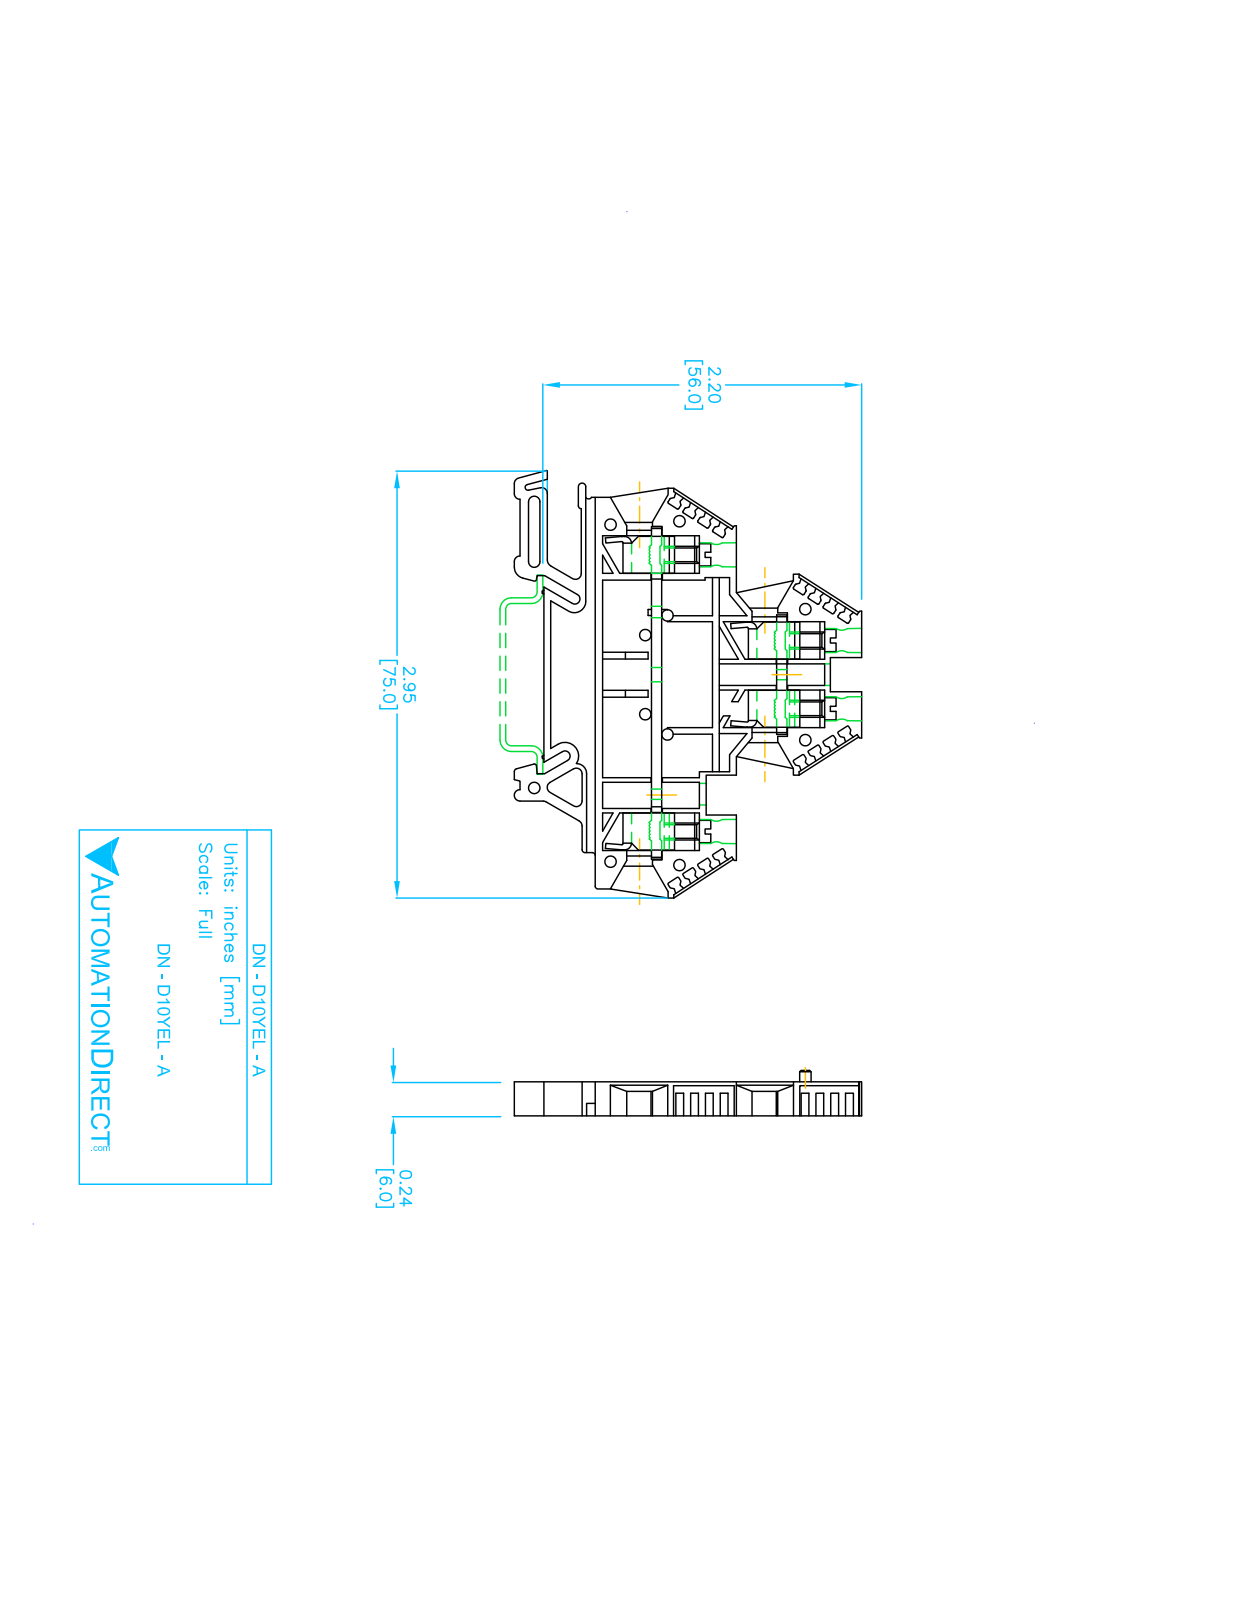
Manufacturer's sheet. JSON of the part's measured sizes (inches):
{"part_name": "DN-D10YEL-A", "step_written_by": "SolidWorks 2017 (AUTOMOTIVE_DESIGN)", "units": "inches", "bodies": {"solids": 1, "faces": 402, "planar": 261, "cylindrical": 141, "other": 0}, "overall_size": [2.957, 2.402, 0.236], "volume_in3": 0.9, "surface_area_in2": 14.85, "round_holes": [[0.165, 4], [0.079, 1]], "round_bosses_or_shafts": [[0.146, 4]], "partial_cylinders_radius": [[0.008, 64], [0.039, 13], [0.02, 6], [0.012, 2], [0.035, 2], [0.075, 2], [0.079, 2], [0.004, 1]], "face_to_face_distances": [0.236, 0.079, 0.157, 0.354, 0.059, 0.024, 0.031, 0.047, 0.976, 0.071], "hole_center_spacings": [0.472, 0.593, 0.848, 1.065, 1.321, 1.913]}
